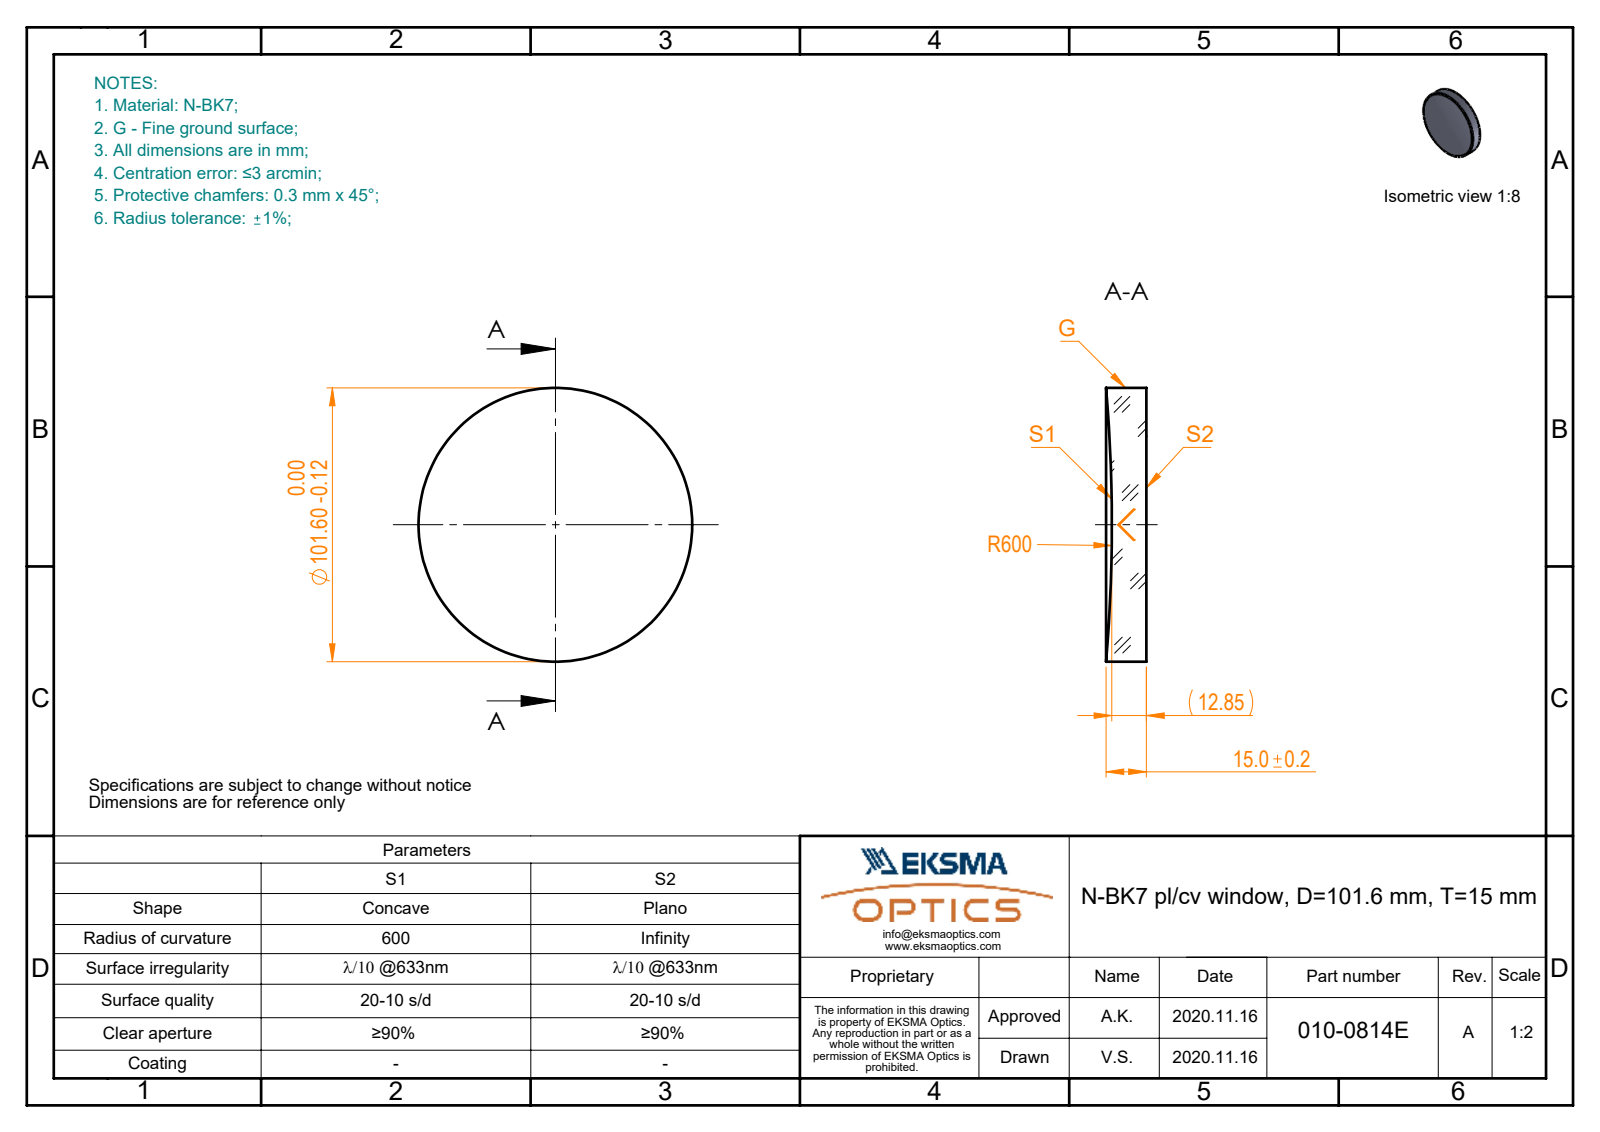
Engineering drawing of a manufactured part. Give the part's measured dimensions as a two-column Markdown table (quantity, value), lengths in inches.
| quantity | value |
| --- | --- |
| part name | 010-0814E_N-BK7_PCV_window |
| STEP written by | SolidWorks 2019 (CONFIG_CONTROL_DESIGN) |
| units | inches |
| bodies | 1 solid, 5 faces (1 planar, 2 cylindrical, 2 other) |
| overall size | 4 × 4 × 0.591 |
| volume | 6.888 in³ |
| surface area | 32.58 in² |
| round bosses / shafts (diameter × count) | 4 × 1 |
